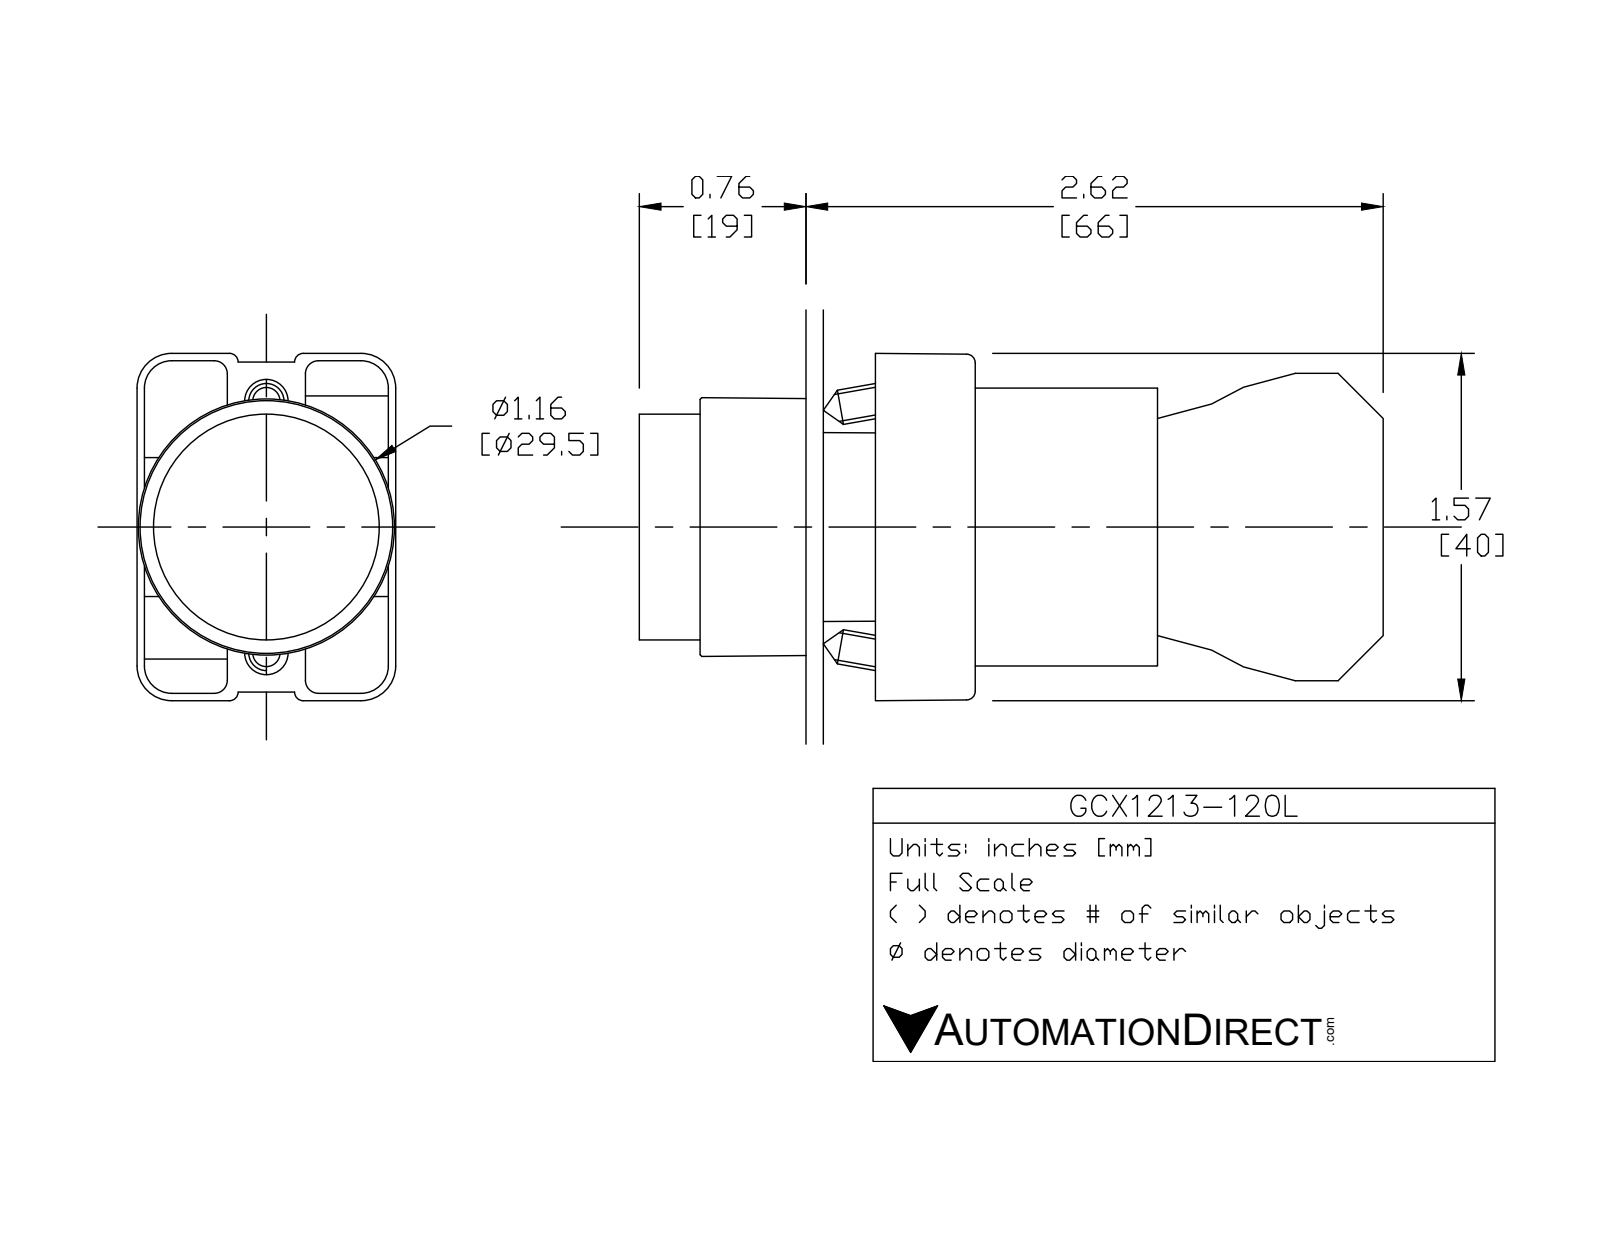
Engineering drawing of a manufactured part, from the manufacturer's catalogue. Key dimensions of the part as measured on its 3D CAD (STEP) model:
Part name (STEP PRODUCT): ECX1050; ecx1040; GCX1213L OPERATOR; GCX1213-120L (+1 more)
STEP written by: SolidWorks 2016 (AUTOMOTIVE_DESIGN)
Units: inches
Bodies: 7 solids, 425 faces (250 planar, 144 cylindrical, 31 other)
Overall size (bounding box): 3.319 × 1.581 × 1.177
Volume: 2.721 in³ · Surface area: 36.32 in²
Round holes (diameter × count): ⌀0.079 ×2, ⌀0.124 ×2, ⌀0.13 ×2, ⌀0.087 ×1, ⌀0.197 ×1, ⌀0.469 ×1, ⌀0.878 ×1, ⌀0.888 ×1, ⌀1.024 ×1
Round bosses / shafts (diameter × count): ⌀0.157 ×4, ⌀1.175 ×1, ⌀1.004 ×1, ⌀0.945 ×1, ⌀0.856 ×1, ⌀0.78 ×1, ⌀0.504 ×1
Partial cylindrical surfaces — rounded edges, fillets, slot ends (radius × count): R0.059 ×24, R0.041 ×12, R0.124 ×12, R0.157 ×12, R0.039 ×8, R0.128 ×2, R0.02 ×1, R0.063 ×1
Main face-to-face distances: 0.827, 0.579, 1.171, 2.02, 1.193, 0.031, 0.033, 0.573, 1.165, 0.593
Hole centre spacings: 0.236, 0.544, 0.472, 0.49
